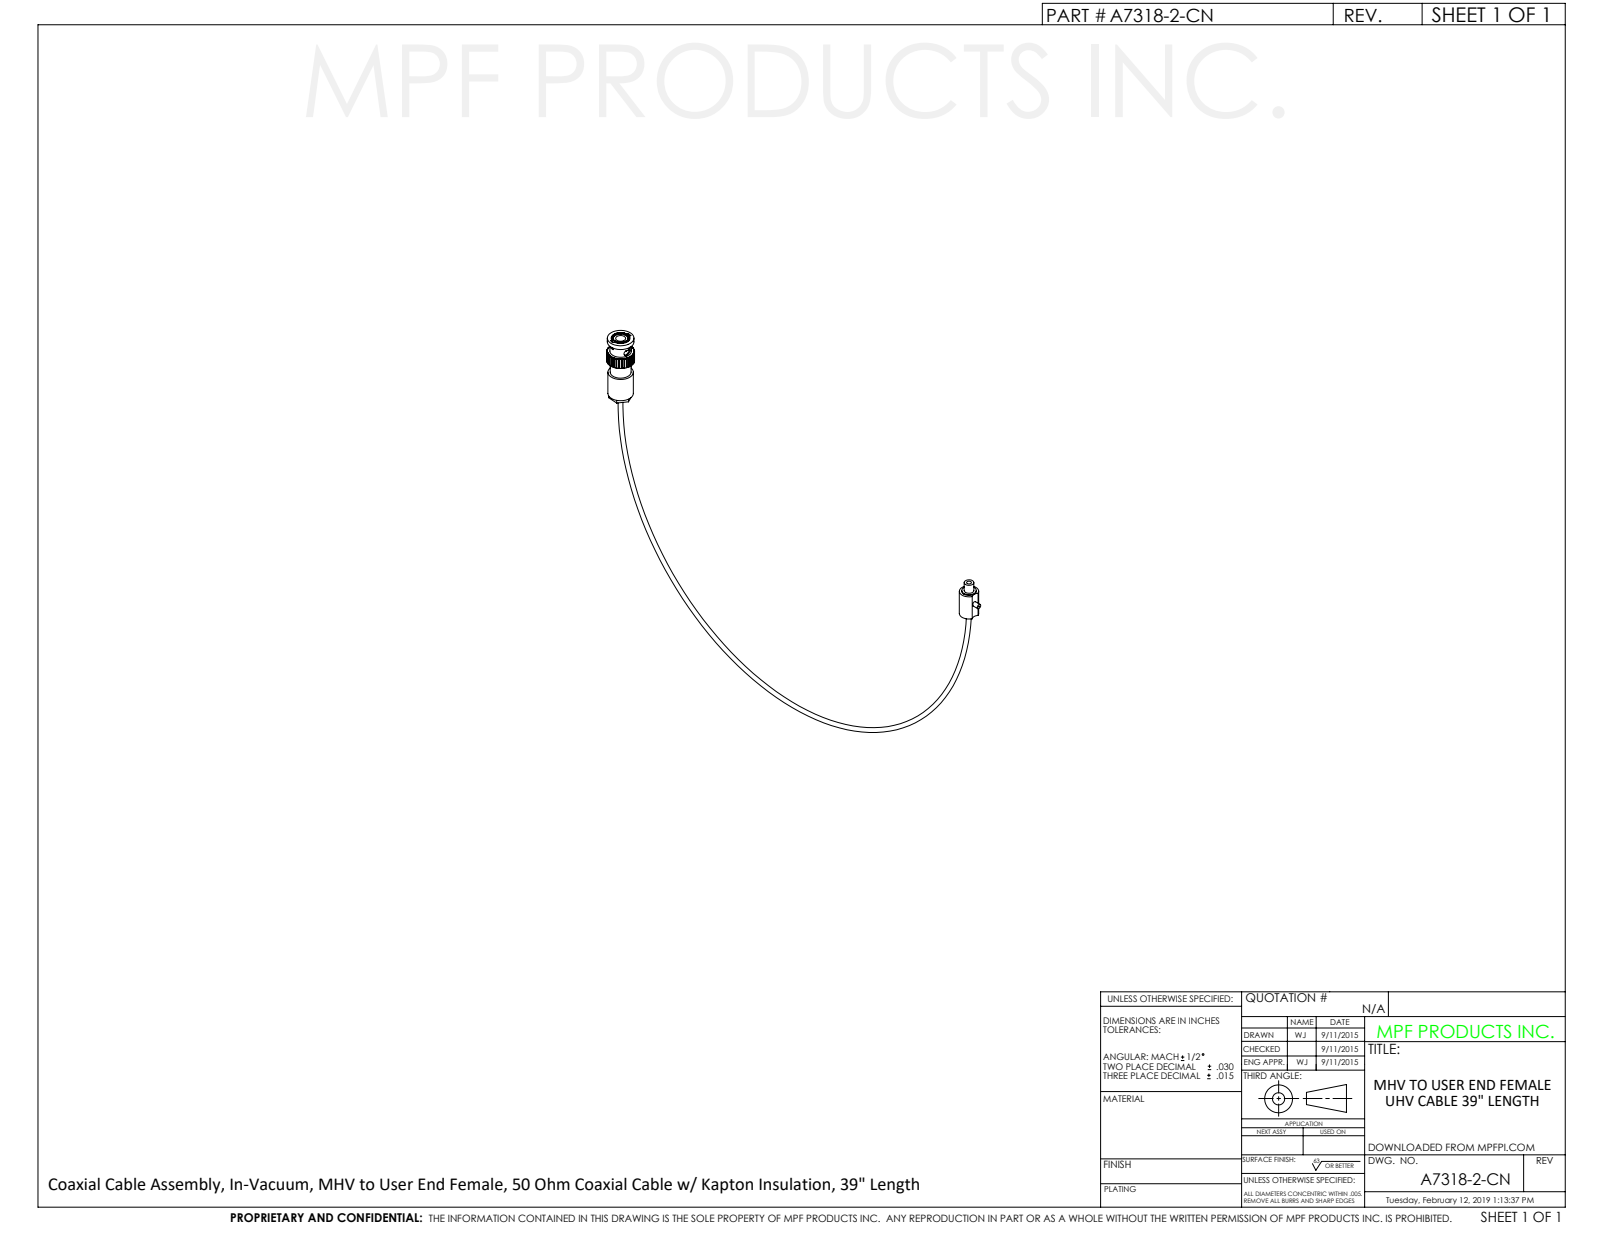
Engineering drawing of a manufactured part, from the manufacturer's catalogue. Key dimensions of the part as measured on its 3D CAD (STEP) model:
Part name (STEP PRODUCT): A7317-2-CN
STEP written by: SolidWorks 2012 (CONFIG_CONTROL_DESIGN)
Units: inches
Bodies: 2 solids, 329 faces (232 planar, 95 cylindrical, 2 other)
Overall size (bounding box): 6.078 × 3.881 × 0.575
Volume: 0.316 in³ · Surface area: 8.094 in²
Round holes (diameter × count): ⌀0.067 ×1, ⌀0.074 ×1, ⌀0.158 ×1, ⌀0.194 ×1, ⌀0.39 ×1
Round bosses / shafts (diameter × count): ⌀0.55 ×1, ⌀0.525 ×1, ⌀0.445 ×1, ⌀0.43 ×1, ⌀0.428 ×1, ⌀0.308 ×1, ⌀0.233 ×1, ⌀0.134 ×1
Partial cylindrical surfaces — rounded edges, fillets, slot ends (radius × count): R0.068 ×1, R0.15 ×1, R0.151 ×1, R0.287 ×1
Main face-to-face distances: 0.978, 0.693, 0.285, 0.1, 0.014, 0.54, 0.653, 0.041, 0.325, 0.878
Hole centre spacings: 5.576
